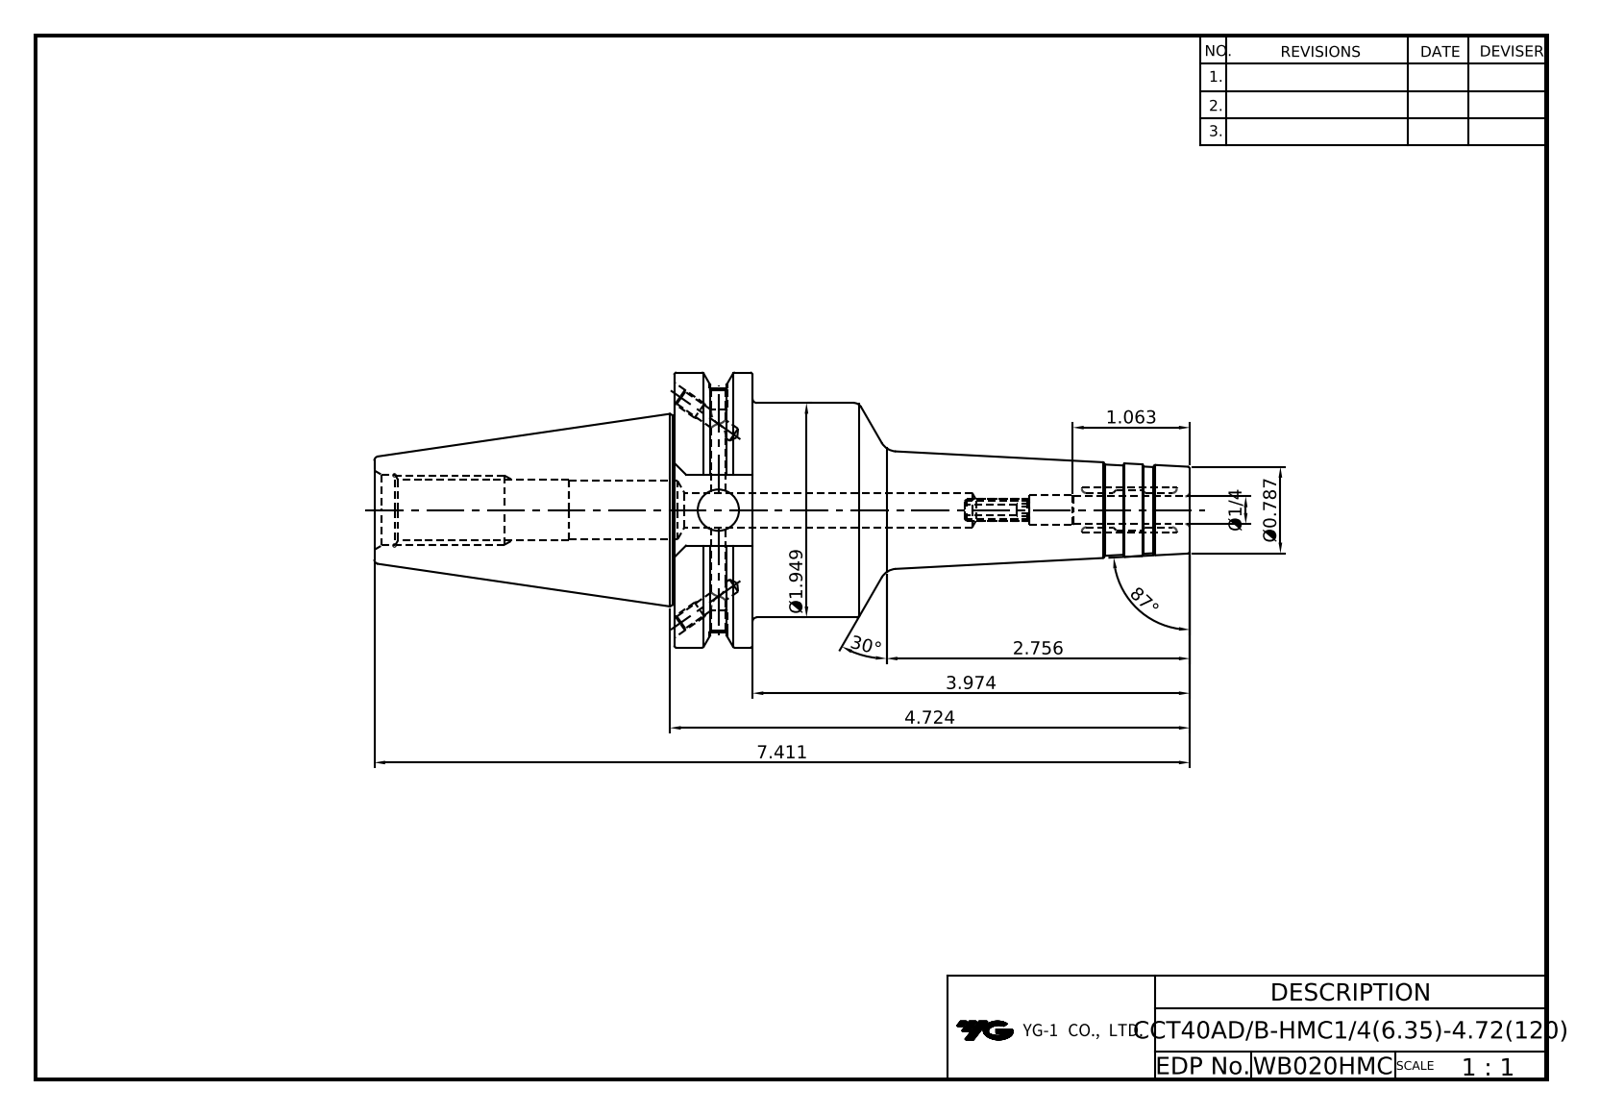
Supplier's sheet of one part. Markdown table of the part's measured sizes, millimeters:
| quantity | value |
| --- | --- |
| part name | LO-CCT40ADB-HMC6.35-120 |
| STEP written by | Autodesk Inventor 2025 (AUTOMOTIVE_DESIGN) |
| units | millimeters |
| bodies | 1 solid, 107 faces (36 planar, 30 cylindrical, 41 other) |
| overall size | 188.25 × 63.5 × 61.09 |
| volume | 186 777 mm³ |
| surface area | 31 955 mm² |
| round holes (diameter × count) | 3.24 × 4, 4 × 2, 4.2 × 2, 4.13 × 1, 6.35 × 1, 6.8 × 1, 8 × 1, 9.53 × 1, 13 × 1, 13.39 × 1, 16.3 × 1 |
| round bosses / shafts (diameter × count) | 63.5 × 1, 49.5 × 1 |
| partial cylindrical surfaces (radius × count) | 8.19 × 1, 28.15 × 1 |
| main face-to-face distances | 18.05, 119, 100.95, 47.6, 16.38, 69.25, 87.3, 188.25, 81.3, 12.05 |
